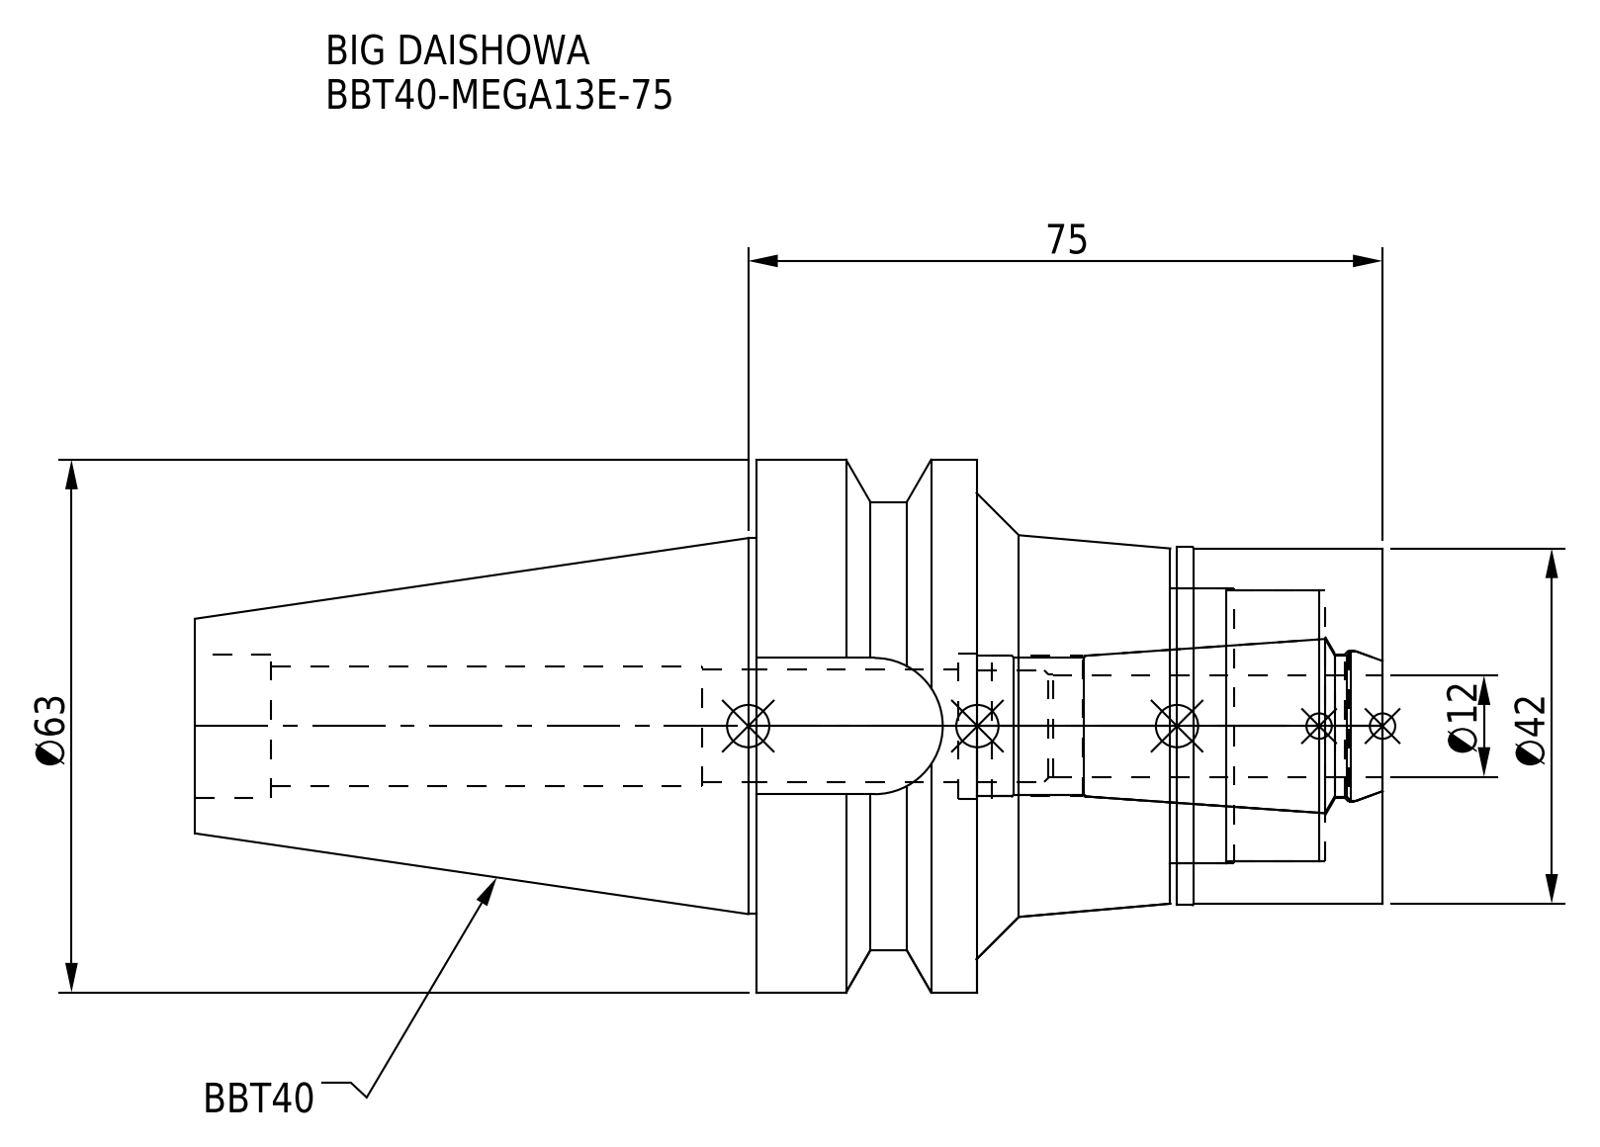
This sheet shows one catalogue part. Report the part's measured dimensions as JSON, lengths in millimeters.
{"part_name": "MEN13_1.stp; BBT40-MEGA13E-75_1.stp; DXF_TEMP_ASSY_ASM_4_ASM.stp; BBT40-MEGA13E-75-120-FreeParts (+3 more)", "step_written_by": "SolidWorks 2019 (CONFIG_CONTROL_DESIGN)", "units": "millimeters", "bodies": {"solids": 2, "faces": 78, "planar": 20, "cylindrical": 38, "other": 20}, "overall_size": [140.4, 63, 63], "volume_mm3": 179202, "surface_area_mm2": 36932, "round_holes": [[13.3, 1], [14.2, 1], [16.6, 1], [17, 1], [17.2, 1], [17.9, 1], [32, 1], [32.5, 1]], "round_bosses_or_shafts": [[63, 1], [53, 1], [44.45, 1], [42.3, 1], [42, 1]], "partial_cylinders_radius": [[8.05, 1]], "face_to_face_distances": [74, 48, 26, 25.1, 24.3, 23.7, 49.7, 0.8, 22.9, 48.9]}
